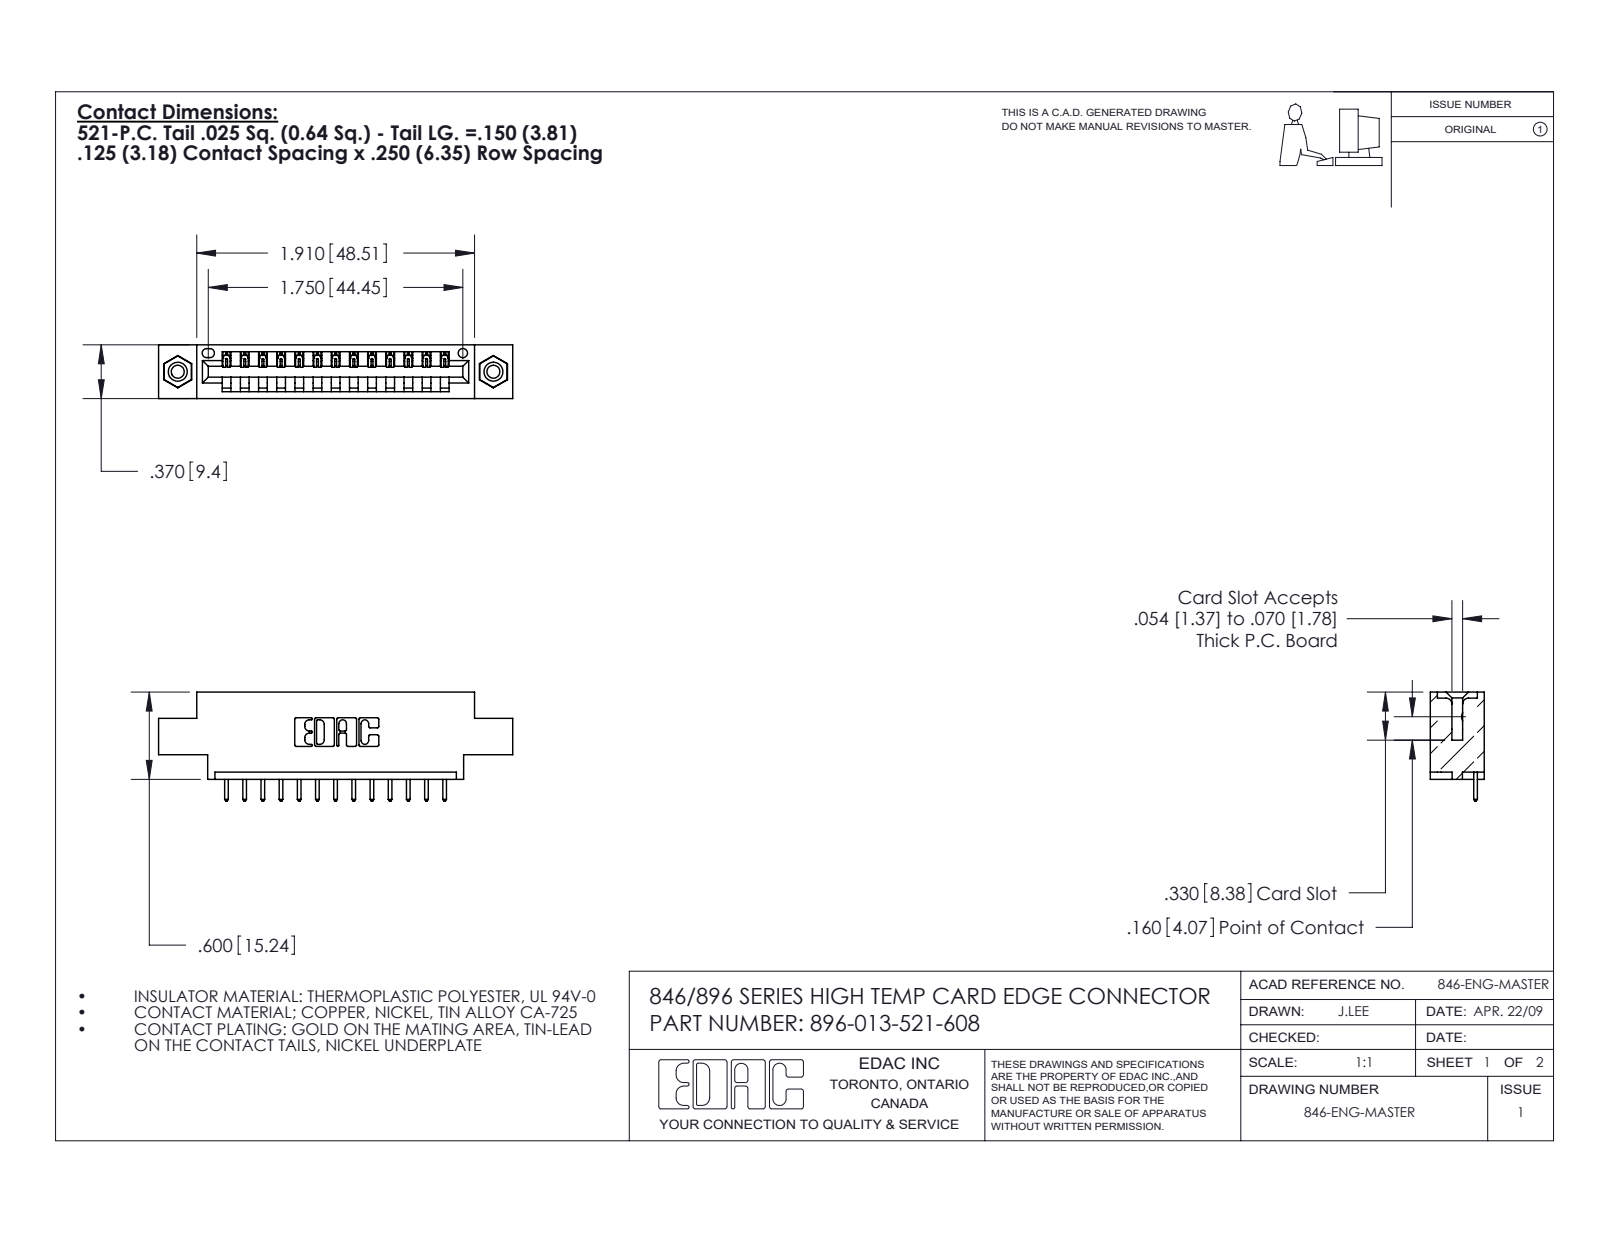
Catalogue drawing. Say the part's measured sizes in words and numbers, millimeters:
The part is named "345-292-001_345-293-121; 345-250-001_345-250-003-102; 346 Part_0.170 Offset - 0.156 Dia-TI; 396-013-521-608". Its 3-D file was written by "SolidWorks 2016 (CONFIG_CONTROL_DESIGN)". It is 16 solids with 940 faces: 632 planar, 292 cylindrical and 16 other. Overall it measures 61.8 by 19.1 by 9.4 millimeters. Its volume is 5 520 cubic millimeters and its surface area 6 626 square millimeters. Round holes: 2 of diameter 2.3, 2 of diameter 3.2, 2 of diameter 4, 1 of diameter 1.6. Round bosses or shafts: 2 of diameter 3.9. Partial cylindrical surfaces (rounded edges, fillets, slot ends): 26 of radius 0.2, 26 of radius 0.3, 22 of radius 0.3, 6 of radius 0.2, 6 of radius 0.8, 3 of radius 0.7, 2 of radius 0.8, 2 of radius 1. The main face-to-face distances are 9.4, 6.4, 1.2, 8.2, 5.6, 3.8, 1.8, 7.6, 0.6, 2.5. The hole center spacings are 6.2, 49.9, 55.1.
